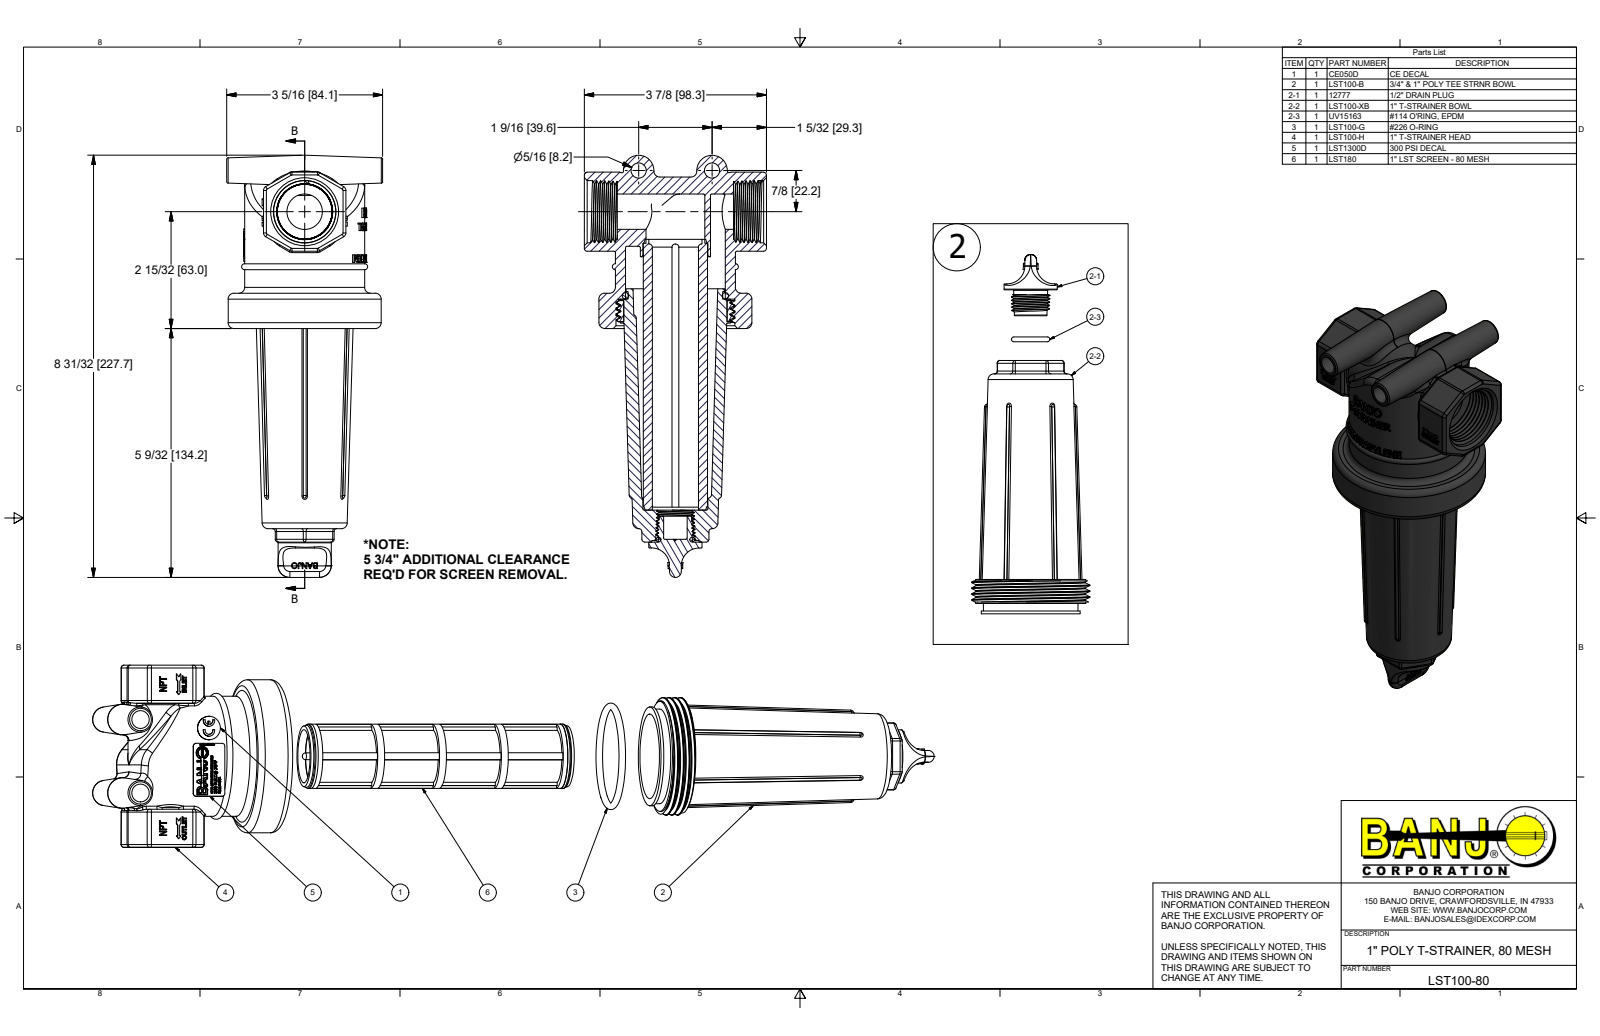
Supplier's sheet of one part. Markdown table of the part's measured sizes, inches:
| quantity | value |
| --- | --- |
| part name | LST100-80; CE050D; LST100-B; LST100-XB (+6 more) |
| STEP written by | Autodesk Inventor 2018 (AUTOMOTIVE_DESIGN) |
| units | inches |
| bodies | 9 solids, 2849 faces (1566 planar, 255 cylindrical, 1028 other) |
| overall size | 38.886 × 14.249 × 3.312 |
| volume | 19.13 in³ |
| surface area | 480.5 in² |
| round holes (diameter × count) | 0.181 × 1, 0.257 × 1, 0.5 × 1, 0.75 × 1, 0.98 × 1, 1.005 × 1, 1.1 × 1, 1.25 × 1, 1.38 × 1, 2.12 × 1, 2.195 × 1, 2.396 × 1 |
| round bosses / shafts (diameter × count) | 3.25 × 1, 2.55 × 1, 2.5 × 1, 2.34 × 1, 2.1 × 1, 2.01 × 1, 1.49 × 1, 1.47 × 1 |
| partial cylindrical surfaces (radius × count) | 0.06 × 52, 0.03 × 11, 0.094 × 8, 0.075 × 4, 0.026 × 2, 0.033 × 2, 0.035 × 2, 0.063 × 2 |
| main face-to-face distances | 0.15, 1.75, 1.35, 1.2, 0.75, 0.25, 0.7, 1.5, 4.45, 0.625 |
